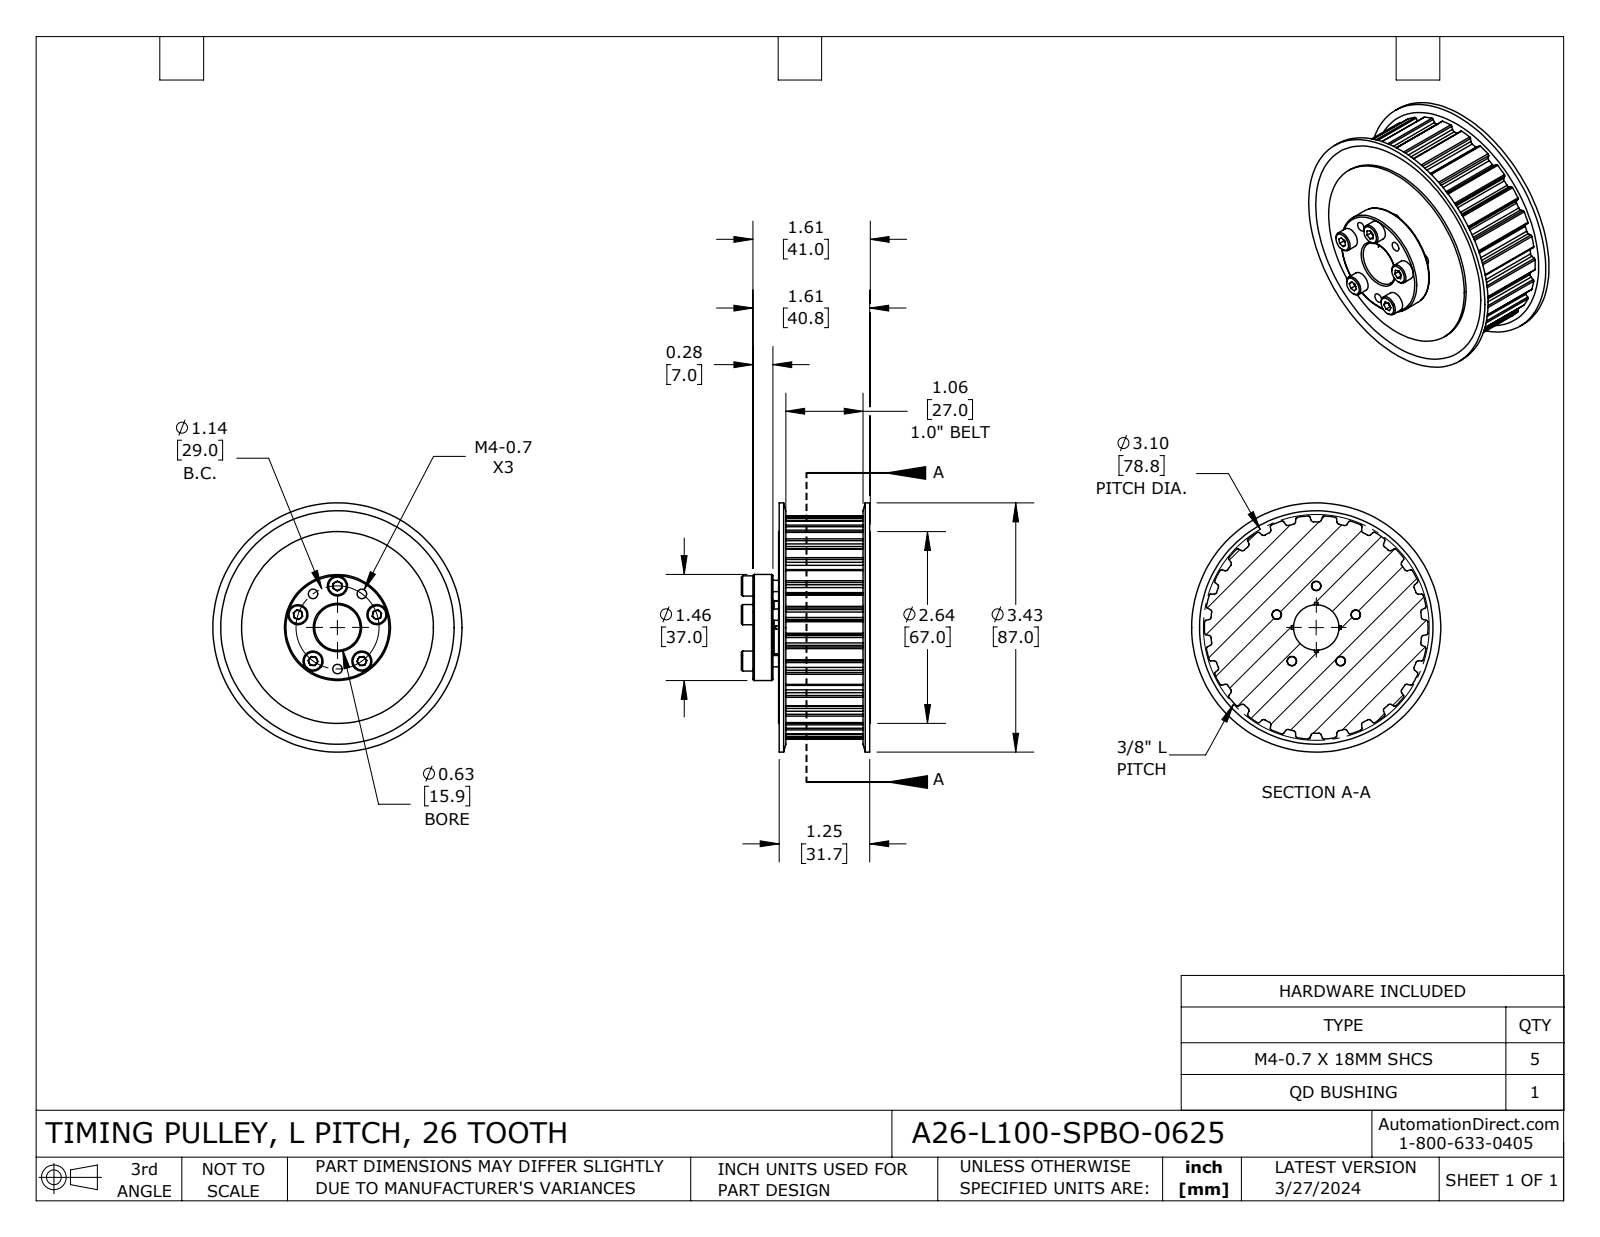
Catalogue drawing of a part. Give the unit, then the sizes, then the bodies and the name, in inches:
Units: inches
Overall size (bounding box): 3.425 × 3.425 × 1.772
Round holes (diameter × count): ⌀0.13 ×8, ⌀0.177 ×5, ⌀0.625 ×1, ⌀0.727 ×1
Round bosses / shafts (diameter × count): ⌀0.276 ×5, ⌀0.157 ×5, ⌀3.425 ×1, ⌀2.638 ×1, ⌀1.457 ×1
Partial cylindrical surfaces — rounded edges, fillets, slot ends (radius × count): R0.021 ×52, R0.034 ×52, R1.453 ×1, R1.537 ×1
Main face-to-face distances: 0.035, 1.224, 1.26, 1.189, 0.098, 1.161, 0.063, 1.126, 1.063, 0.354
Hole centre spacings: 0.571, 1.086, 0.353, 0.924, 0.671, 1.142, 0.671
Volume: 9.09 in³ · Surface area: 47.36 in²
Bodies: 1 solid, 457 faces (151 planar, 244 cylindrical, 62 other)
Part name (STEP PRODUCT): A26-L100-SPBO-0625
STEP written by: SolidWorks 2021 (CONFIG_CONTROL_DESIGN)
